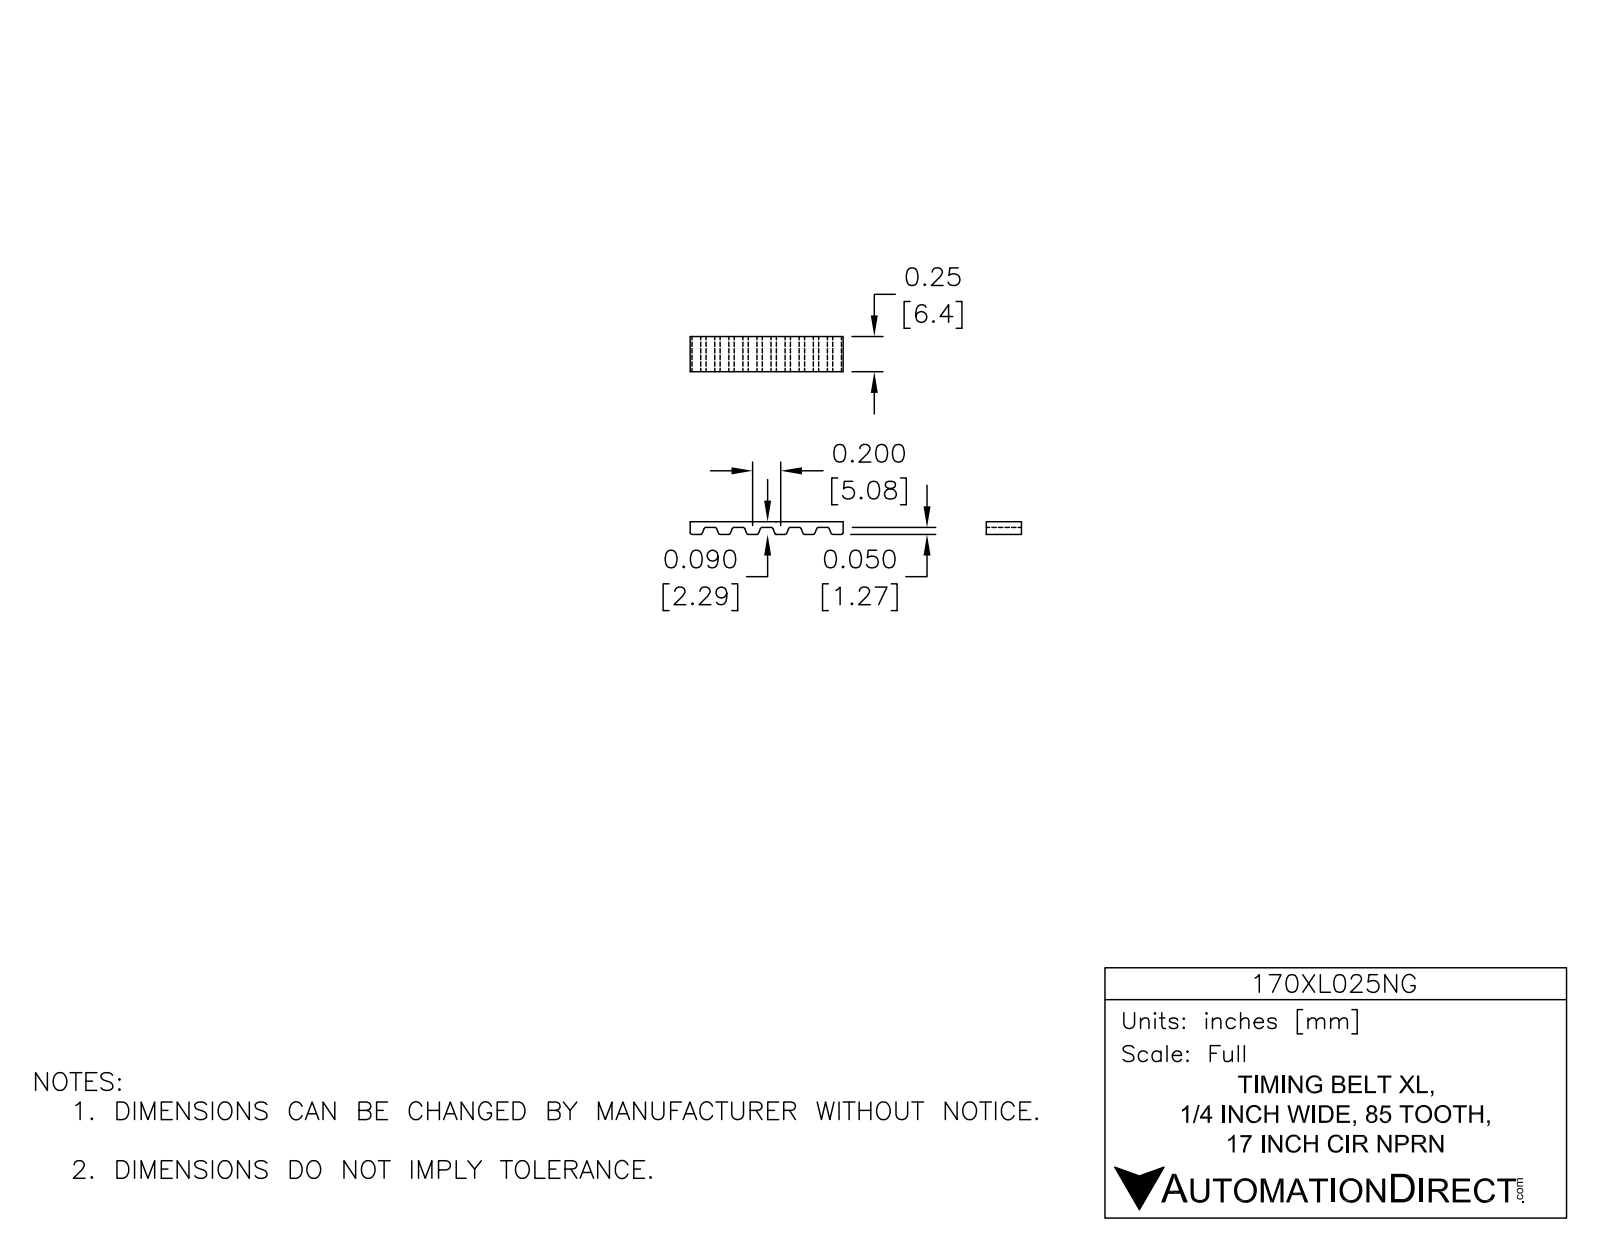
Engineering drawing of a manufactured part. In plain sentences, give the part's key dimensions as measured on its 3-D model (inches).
The part is named "170XL025NG". Its 3-D file was written by "SolidWorks 2014 (AUTOMOTIVE_DESIGN)". It is 1 solid with 719 faces: 298 planar, 421 cylindrical and 0 other. Overall it measures 6.788 by 3 by 0.25 inches. Its volume is 0.231 cubic inches and its surface area 11.46 square inches. Partial cylindrical surfaces (rounded edges, fillets, slot ends): 340 of radius 0.015, 2 of radius 1.46, 2 of radius 1.5. The main face-to-face distances are 3, 0.25, 0.04, 2.96, 2.92, 0.357, 0.535, 0.714, 0.178, 0.893.
